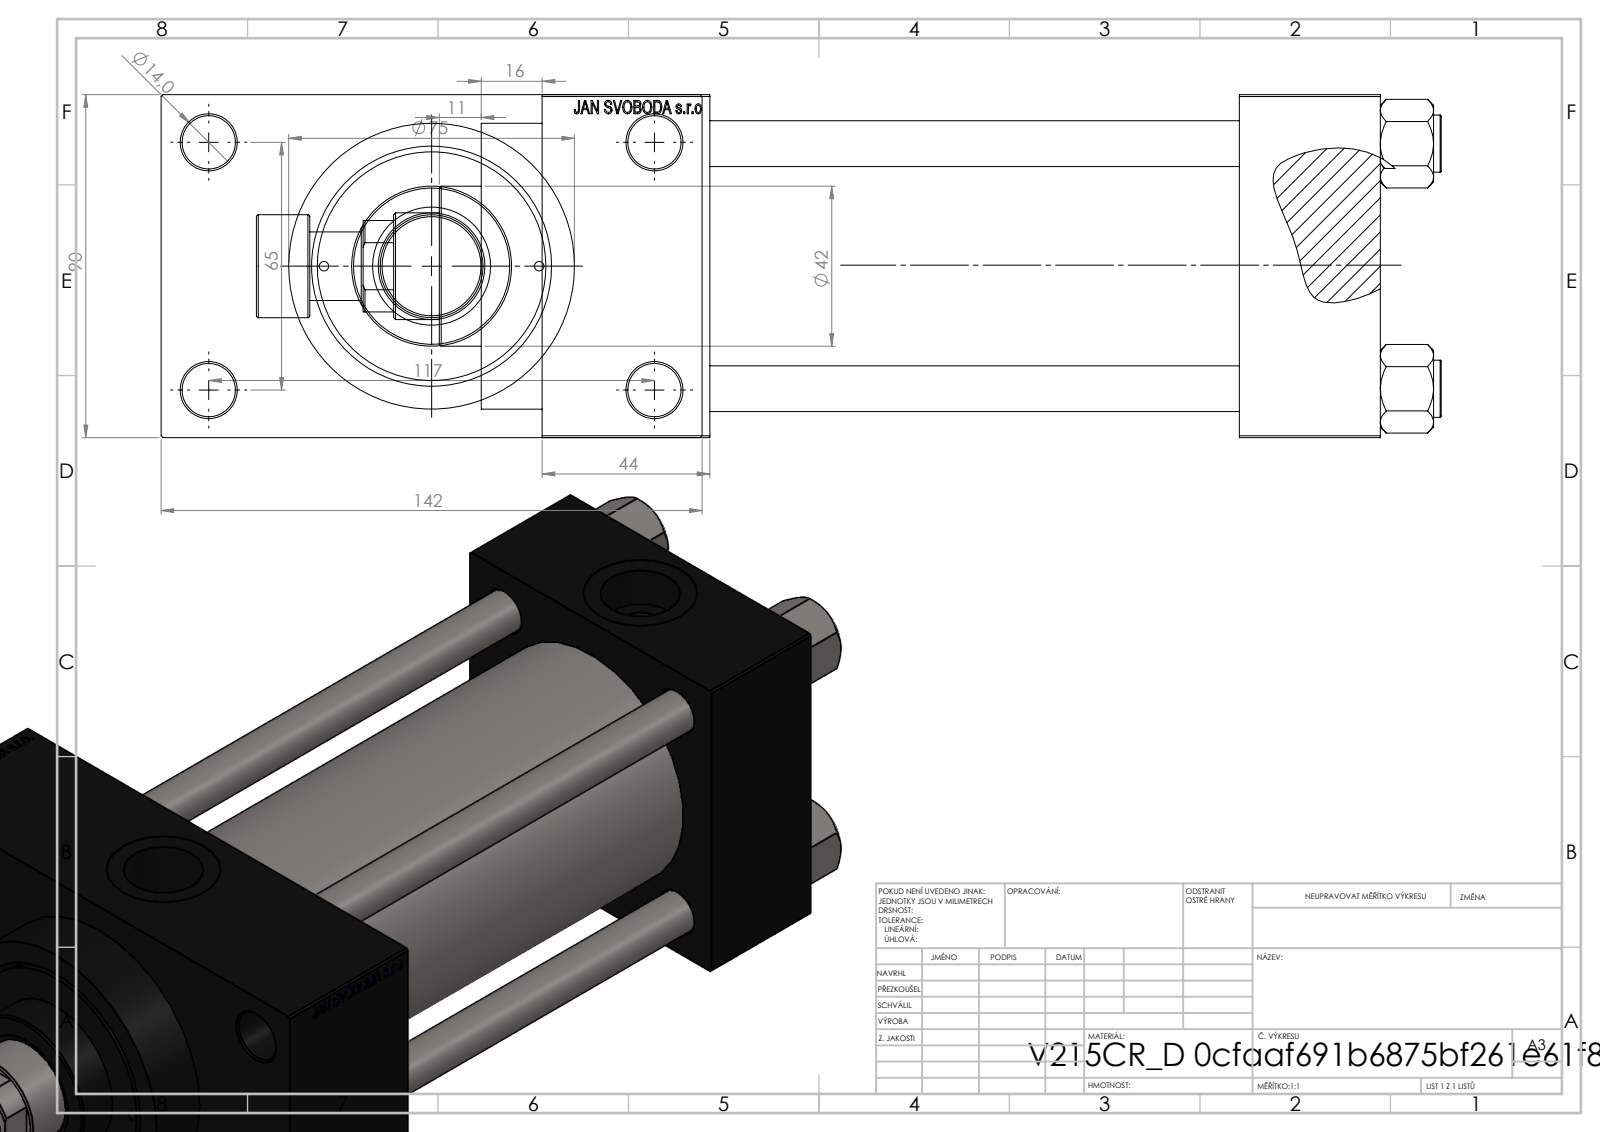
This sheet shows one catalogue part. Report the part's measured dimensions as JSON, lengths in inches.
{"part_name": "V215CR_ROD_END_F; V215CR_VCP_D; V215CR_D_TYCINKA; V215_VC_A (+2 more)", "step_written_by": "SolidWorks 2019 (CONFIG_CONTROL_DESIGN)", "units": "inches", "bodies": {"solids": 12, "faces": 1126, "planar": 503, "cylindrical": 97, "other": 526}, "overall_size": [12.244, 5.591, 3.543], "volume_in3": 76.4, "surface_area_in2": 393.8, "round_holes": [[0.472, 4], [0.551, 4], [0.098, 2], [0.276, 2], [0.825, 2], [1.181, 2], [0.728, 1], [1.102, 1], [1.22, 1], [1.969, 1], [2.362, 1], [2.48, 1]], "round_bosses_or_shafts": [[0.591, 4], [2.953, 1], [2.717, 1], [1.654, 1], [1.063, 1], [0.709, 1]], "face_to_face_distances": [3.543, 5.472, 1.457, 6.929, 7.205, 8.661, 1.732, 1.024, 4.567, 5.591], "hole_center_spacings": [1.037, 1.275, 1.748, 1.79, 2.531, 2.635, 2.694, 2.748]}
